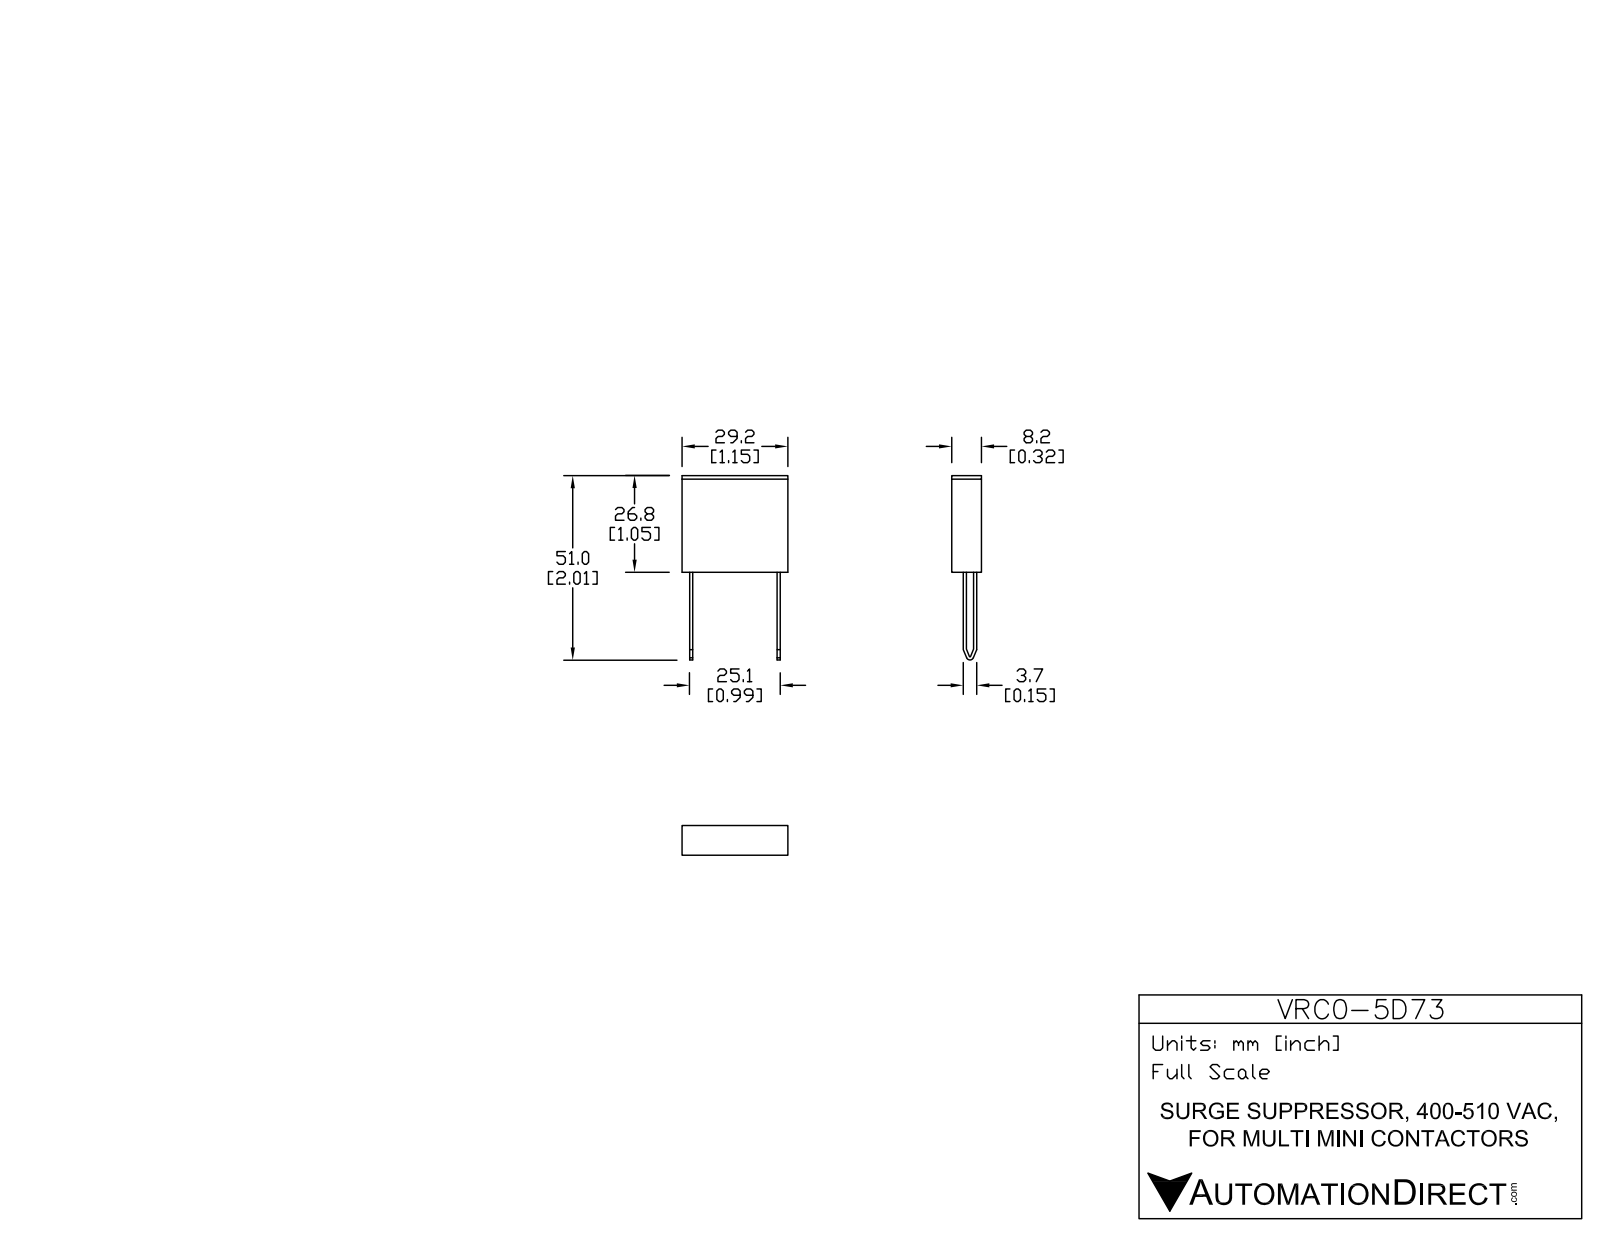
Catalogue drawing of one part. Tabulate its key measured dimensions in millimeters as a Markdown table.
| quantity | value |
| --- | --- |
| part name | VRC0-5D73 |
| STEP written by | SolidWorks 2013 (AUTOMOTIVE_DESIGN) |
| units | millimeters |
| bodies | 1 solid, 34 faces (26 planar, 8 cylindrical, 0 other) |
| overall size | 50.9 × 29.2 × 8.2 |
| volume | 6 463 mm³ |
| surface area | 2 803 mm² |
| partial cylindrical surfaces (radius × count) | 0.15 × 1, 1 × 1 |
| main face-to-face distances | 8.2, 26.7, 29.2, 0.85, 2.1, 27.1, 2.95, 26.25, 24.15, 2.85 |
